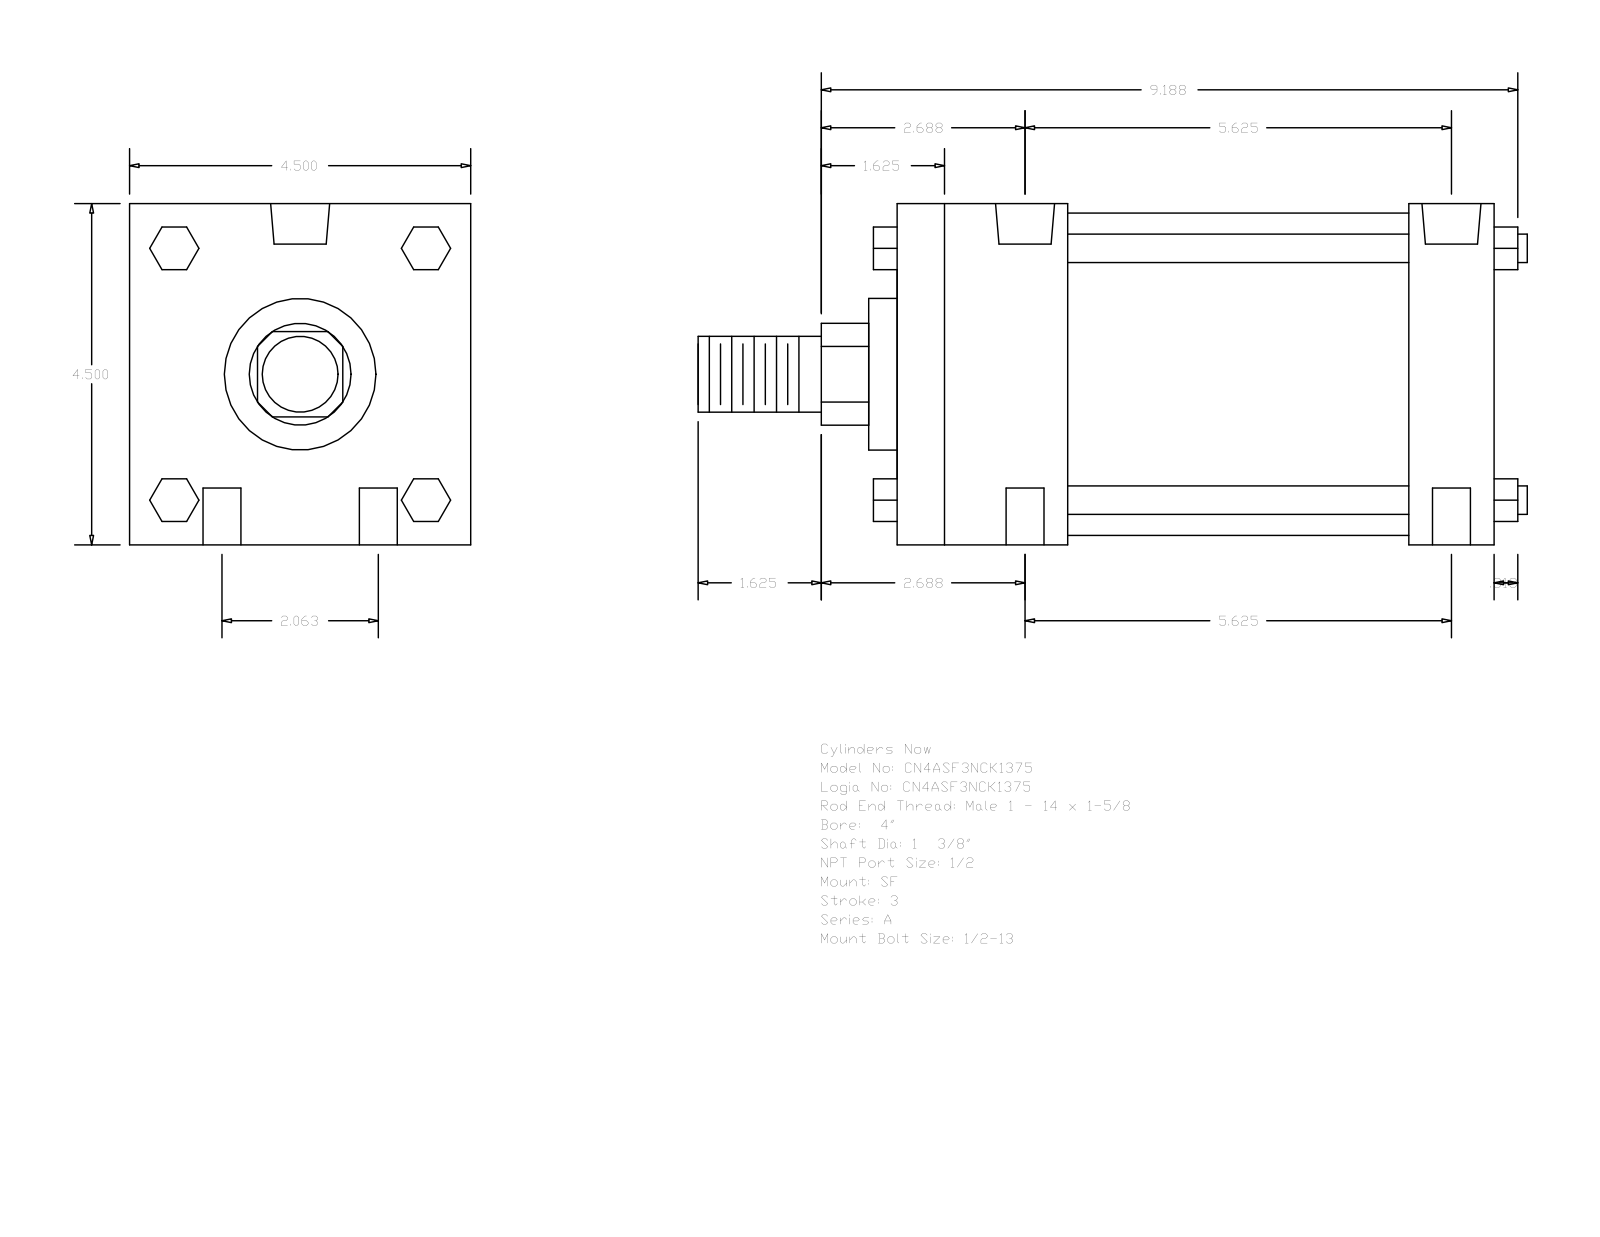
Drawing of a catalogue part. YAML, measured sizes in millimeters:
part_name: "A_SF__0400_1.375"
step_written_by: "GSSL Pune (CONFIG_CONTROL_DESIGN)"
units: millimeters
bodies: {solids: 0, faces: 124, planar: 94, cylindrical: 30, other: 0}
overall_size: [277.81, 114.3, 114.3]
round_holes:
  - {diameter: 12.7, count: 4}
  - {diameter: 8.73, count: 2}
  - {diameter: 19.77, count: 2}
round_bosses_or_shafts:
  - {diameter: 9.53, count: 4}
  - {diameter: 107.95, count: 1}
  - {diameter: 50.8, count: 1}
  - {diameter: 34.92, count: 1}
  - {diameter: 25.4, count: 1}
partial_cylinders:
  - {radius: 17.06, count: 1}
face_to_face_distances: [114.3, 200.03, 57.15, 28.58, 171.45, 142.88, 66.67, 14.29, 9.52, 180.97]
hole_center_spacings: [26.19, 145.26, 142.88, 52.38, 152.18, 136.52]
